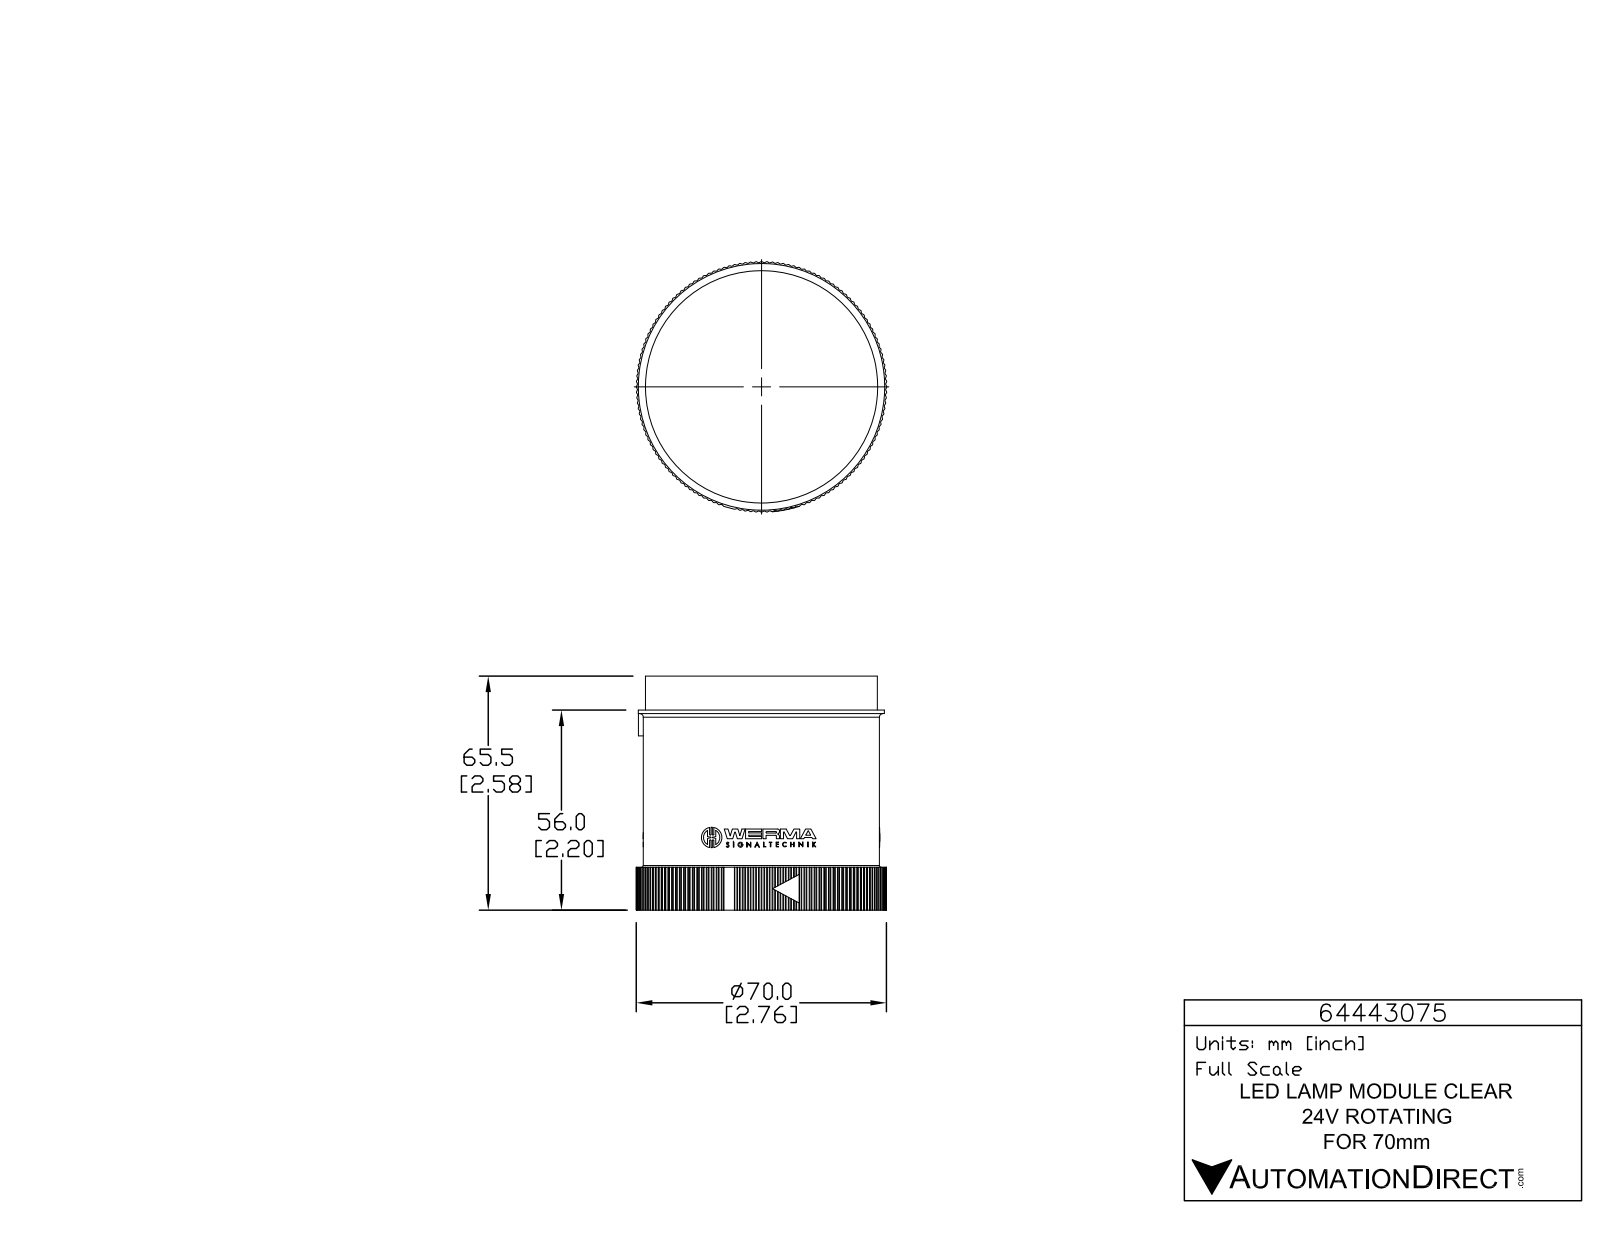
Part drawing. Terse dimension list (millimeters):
name: 64443075
written by: SolidWorks 2015 (AUTOMOTIVE_DESIGN)
unit: mm
bodies: 1 solid, 1400 faces (832 planar, 563 cylindrical, 5 other)
size: 70.2 × 70.2 × 65.5
volume: 197 000 mm³; area: 24 180 mm²
holes: 3× ⌀1, 1× ⌀65.4
bosses: 3× ⌀5.7, 3× ⌀1.4, 1× ⌀69, 1× ⌀66.2, 1× ⌀65
rounds: 285× R0.2, 6× R0.2, 6× R0.2, 6× R0.2, 6× R3.3, 3× R0.1, 3× R0.1, 3× R0.2
face distances: 55.9, 62.3, 9.6, 65.5, 56, 46.4, 9.5, 62.3, 12, 2.4
